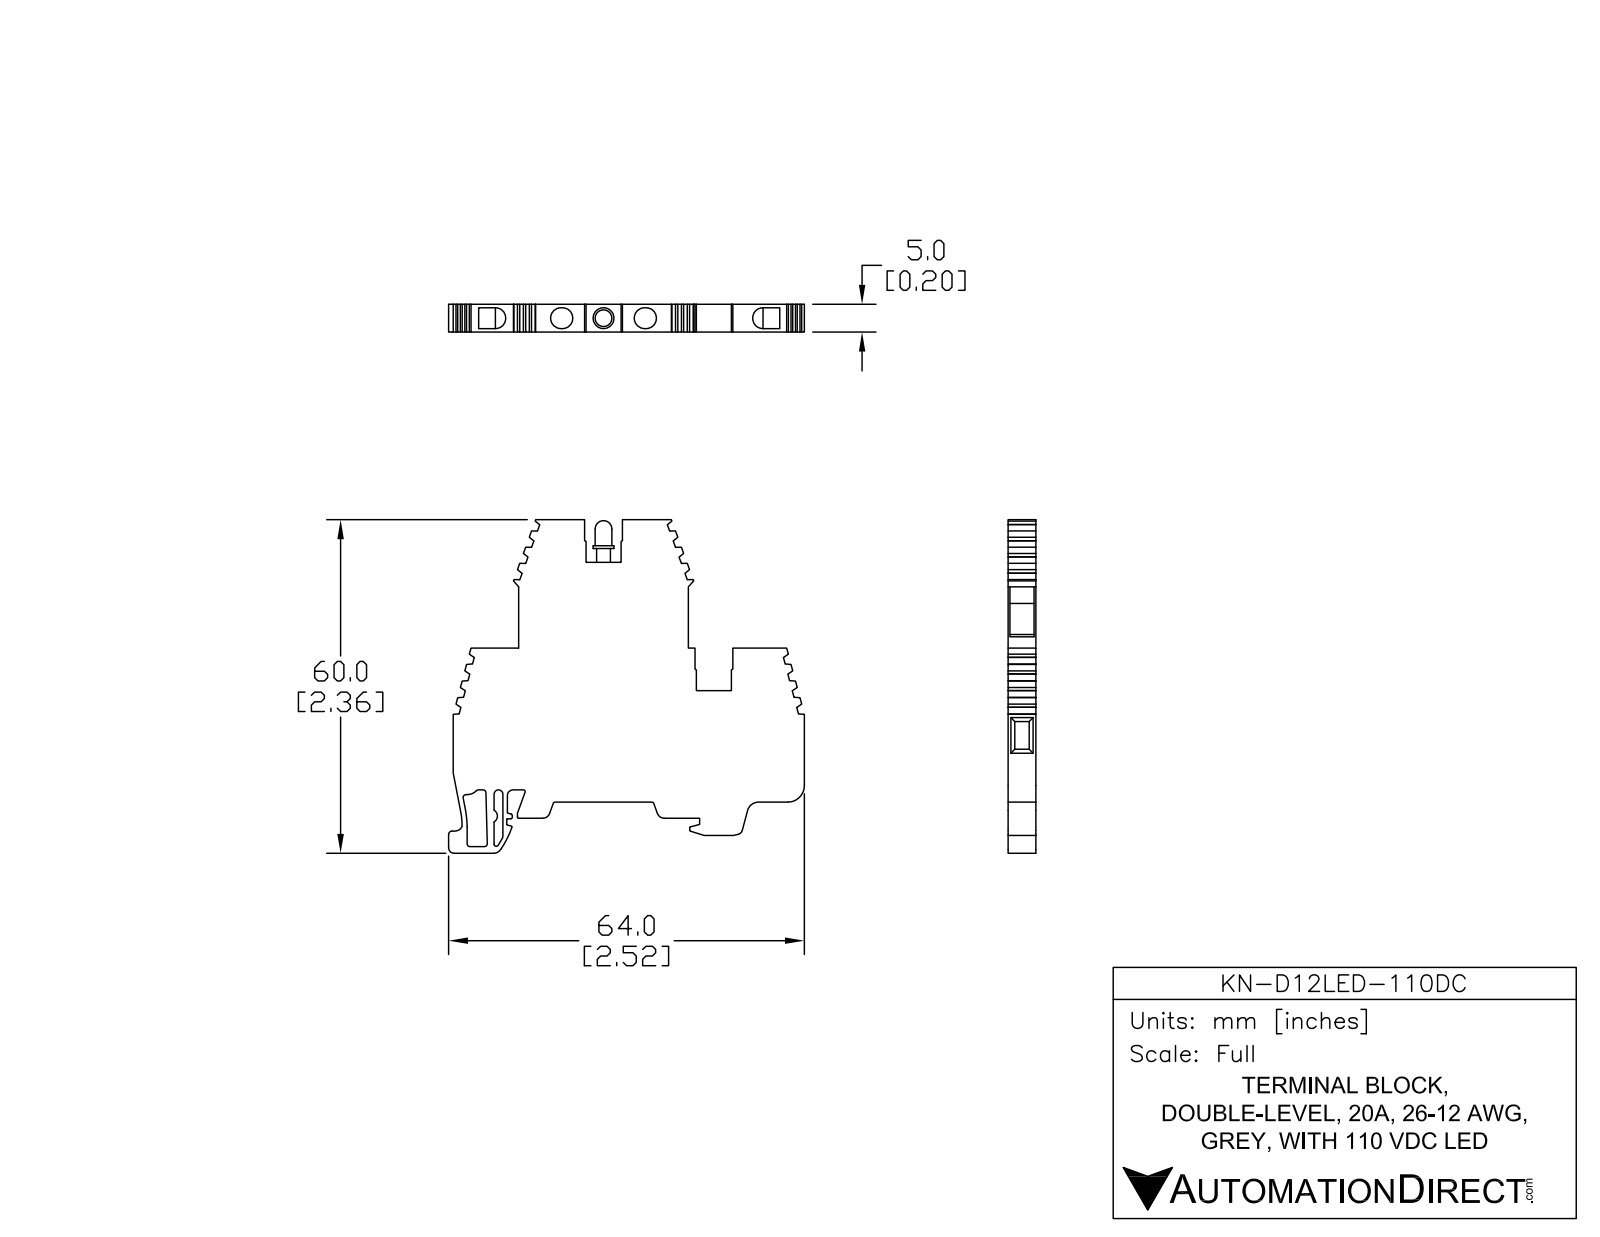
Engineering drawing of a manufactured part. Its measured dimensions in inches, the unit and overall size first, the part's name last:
Units: inches
Overall size (bounding box): 2.521 × 2.362 × 0.197
Round bosses / shafts (diameter × count): ⌀0.148 ×1, ⌀0.118 ×1, ⌀0.098 ×1
Partial cylindrical surfaces — rounded edges, fillets, slot ends (radius × count): R0.02 ×7, R0.012 ×6, R0.074 ×6, R0.008 ×3, R0.039 ×3, R0.024 ×2, R0.016 ×1, R0.031 ×1
Main face-to-face distances: 0.197, 0.184, 0.013, 0.115, 0.909, 0.157, 0.258, 0.782, 0.248, 0.302
Volume: 0.696 in³ · Surface area: 11.04 in²
Bodies: 3 solids, 250 faces (200 planar, 49 cylindrical, 1 other)
Part name (STEP PRODUCT): KN-D12LED-110DC
STEP written by: SolidWorks 2014 (AUTOMOTIVE_DESIGN)
